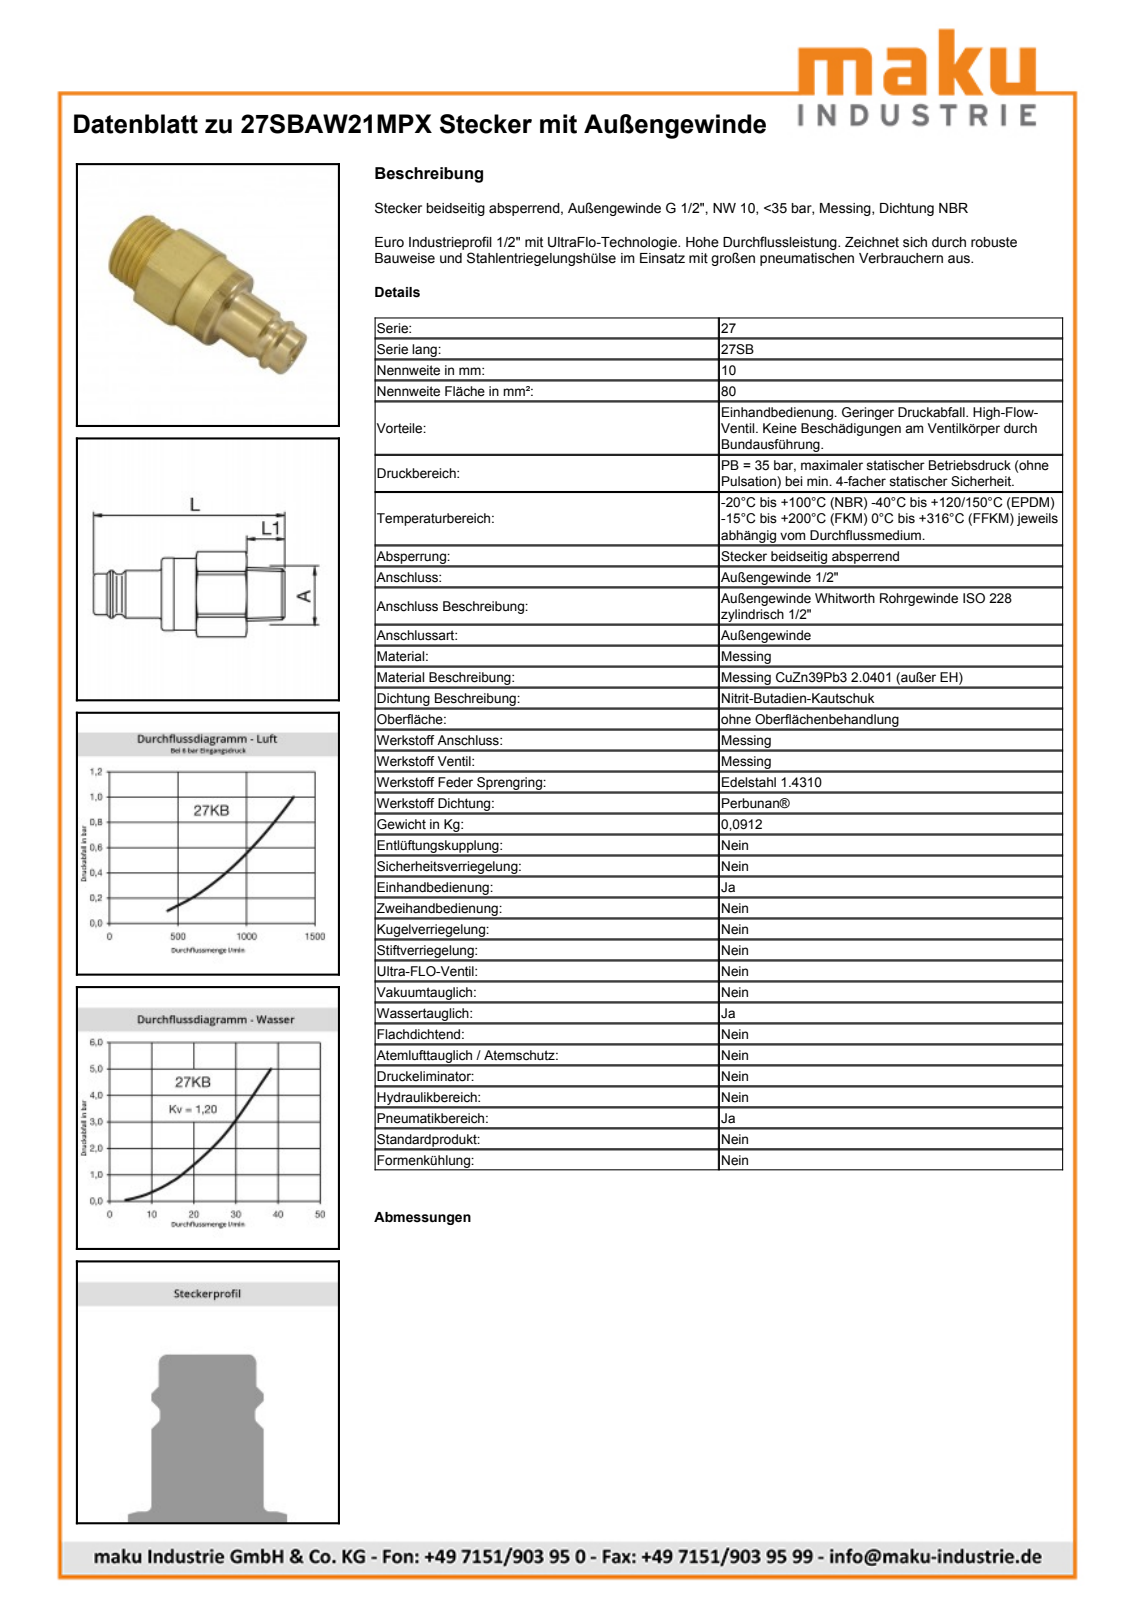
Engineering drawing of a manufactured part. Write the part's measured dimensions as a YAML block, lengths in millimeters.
part_name: "D107077"
step_written_by: "Autodesk Inventor 2013 (AUTOMOTIVE_DESIGN)"
units: millimeters
bodies: {solids: 1, faces: 51, planar: 13, cylindrical: 16, other: 22}
overall_size: [57.4, 26.74, 25.97]
volume: 18401
surface_area: 4740
round_holes:
  - {diameter: 19, count: 1}
  - {diameter: 20.3, count: 1}
round_bosses_or_shafts:
  - {diameter: 23, count: 1}
  - {diameter: 22.75, count: 1}
  - {diameter: 20.96, count: 1}
  - {diameter: 18.5, count: 1}
  - {diameter: 15, count: 1}
  - {diameter: 13, count: 1}
  - {diameter: 12.65, count: 1}
partial_cylinders:
  - {radius: 13.53, count: 1}
face_to_face_distances: [24, 35.9, 23.9, 12, 21.5, 45.4, 57.4, 25.4, 3.9, 20]
